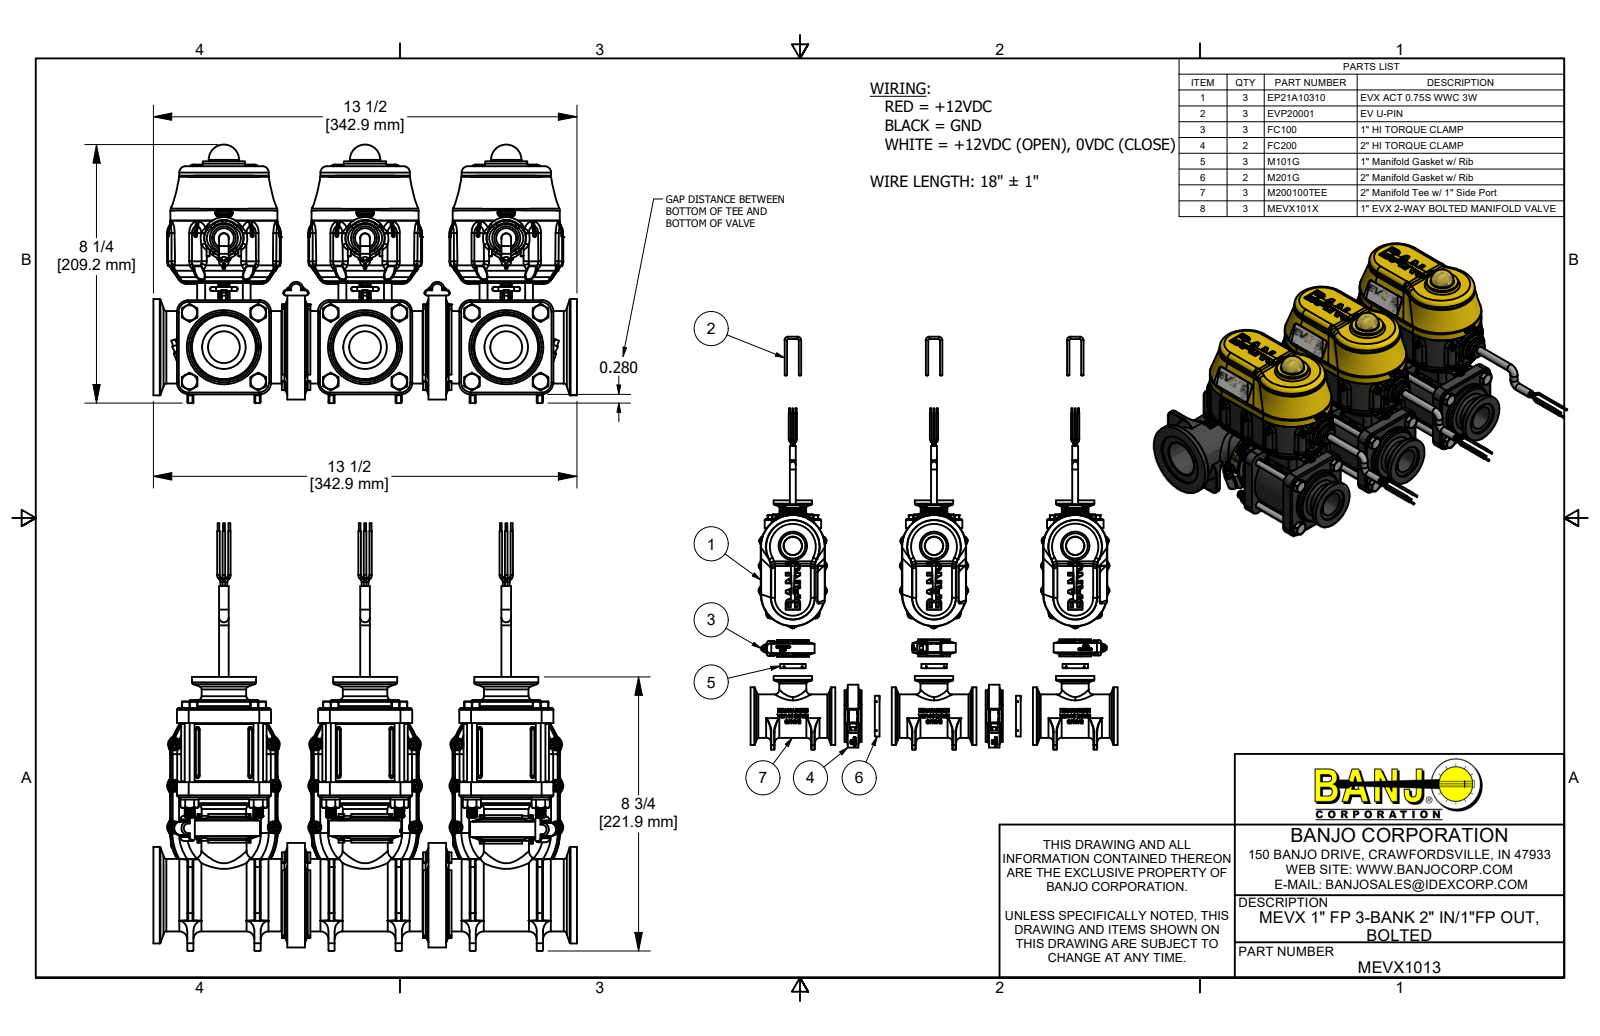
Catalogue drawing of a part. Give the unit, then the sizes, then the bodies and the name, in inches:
Units: inches
Overall size (bounding box): 13.627 × 13.5 × 8.237
Round holes (diameter × count): ⌀0.095 ×33, ⌀0.15 ×33, ⌀0.08 ×21, ⌀0.107 ×12, ⌀0.126 ×12, ⌀0.136 ×12, ⌀0.148 ×12, ⌀0.15 ×12, ⌀0.17 ×12, ⌀0.252 ×12, ⌀0.322 ×12, ⌀0.35 ×12
Round bosses / shafts (diameter × count): ⌀0.268 ×180, ⌀0.25 ×51, ⌀0.08 ×45, ⌀0.14 ×33, ⌀0.108 ×33, ⌀0.085 ×33, ⌀0.058 ×18, ⌀0.313 ×15
Partial cylindrical surfaces — rounded edges, fillets, slot ends (radius × count): R0.013 ×540, R0.04 ×435, R0.01 ×258, R0.03 ×196, R0.02 ×176, R0.005 ×135, R0.06 ×114, R0.08 ×84
Main face-to-face distances: 4.5, 0.1, 2.565, 0.48, 9, 0.06, 0.211, 0.151, 2.365, 0.995
Hole centre spacings: 4.5, 1.662, 1.891, 2.656, 2.715, 9, 2.69, 3.366
Volume: 202.7 in³ · Surface area: 2 200 in²
Bodies: 301 solids, 37388 faces (9706 planar, 10958 cylindrical, 16724 other)
Part name (STEP PRODUCT): MEVX1013; EP21A10310; EP10310; IRF4905 (+8 more)
STEP written by: Autodesk Inventor 2019 (AUTOMOTIVE_DESIGN)
